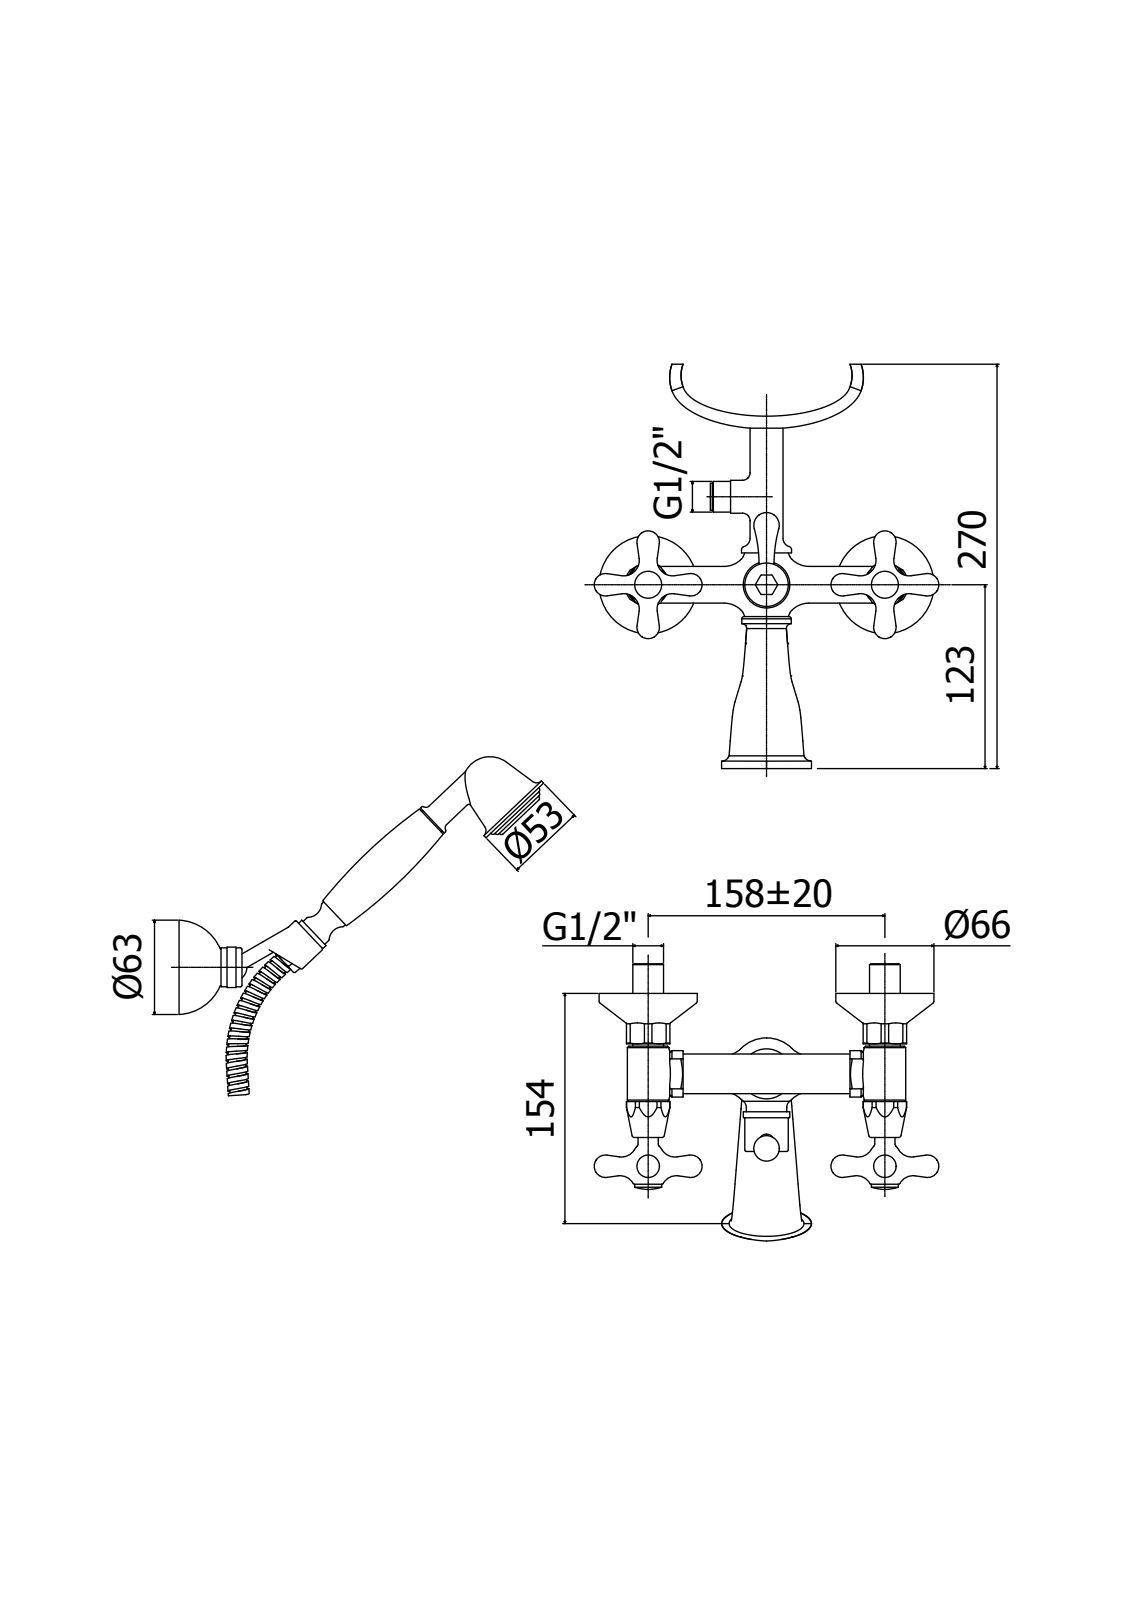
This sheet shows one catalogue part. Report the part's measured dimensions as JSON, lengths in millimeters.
{"part_name": "IRV023CR", "step_written_by": "CREO PARAMETRIC BY PTC INC, 2020044 (CONFIG_CONTROL_DESIGN)", "units": "millimeters", "bodies": {"solids": 4, "faces": 895, "planar": 212, "cylindrical": 172, "other": 511}, "overall_size": [413.37, 346.5, 243.29], "volume_mm3": 543383, "surface_area_mm2": 188451, "round_holes": [[8, 2], [15.7, 2], [17, 2], [18.63, 2], [19, 2], [20.8, 2], [21.5, 2], [23, 2], [9, 1], [14.5, 1], [15.4, 1], [15.5, 1]], "round_bosses_or_shafts": [[18, 3], [65.5, 2], [29, 2], [27.8, 2], [27, 2], [24.5, 2], [22, 2], [13.5, 2]], "partial_cylinders_radius": [[10, 2], [14.5, 2], [15.5, 2], [7.35, 1]], "face_to_face_distances": [26.5, 33.7, 6.75, 66.95, 33.25, 40.45, 29, 5.25, 31.75, 38.57], "hole_center_spacings": [79, 158]}
